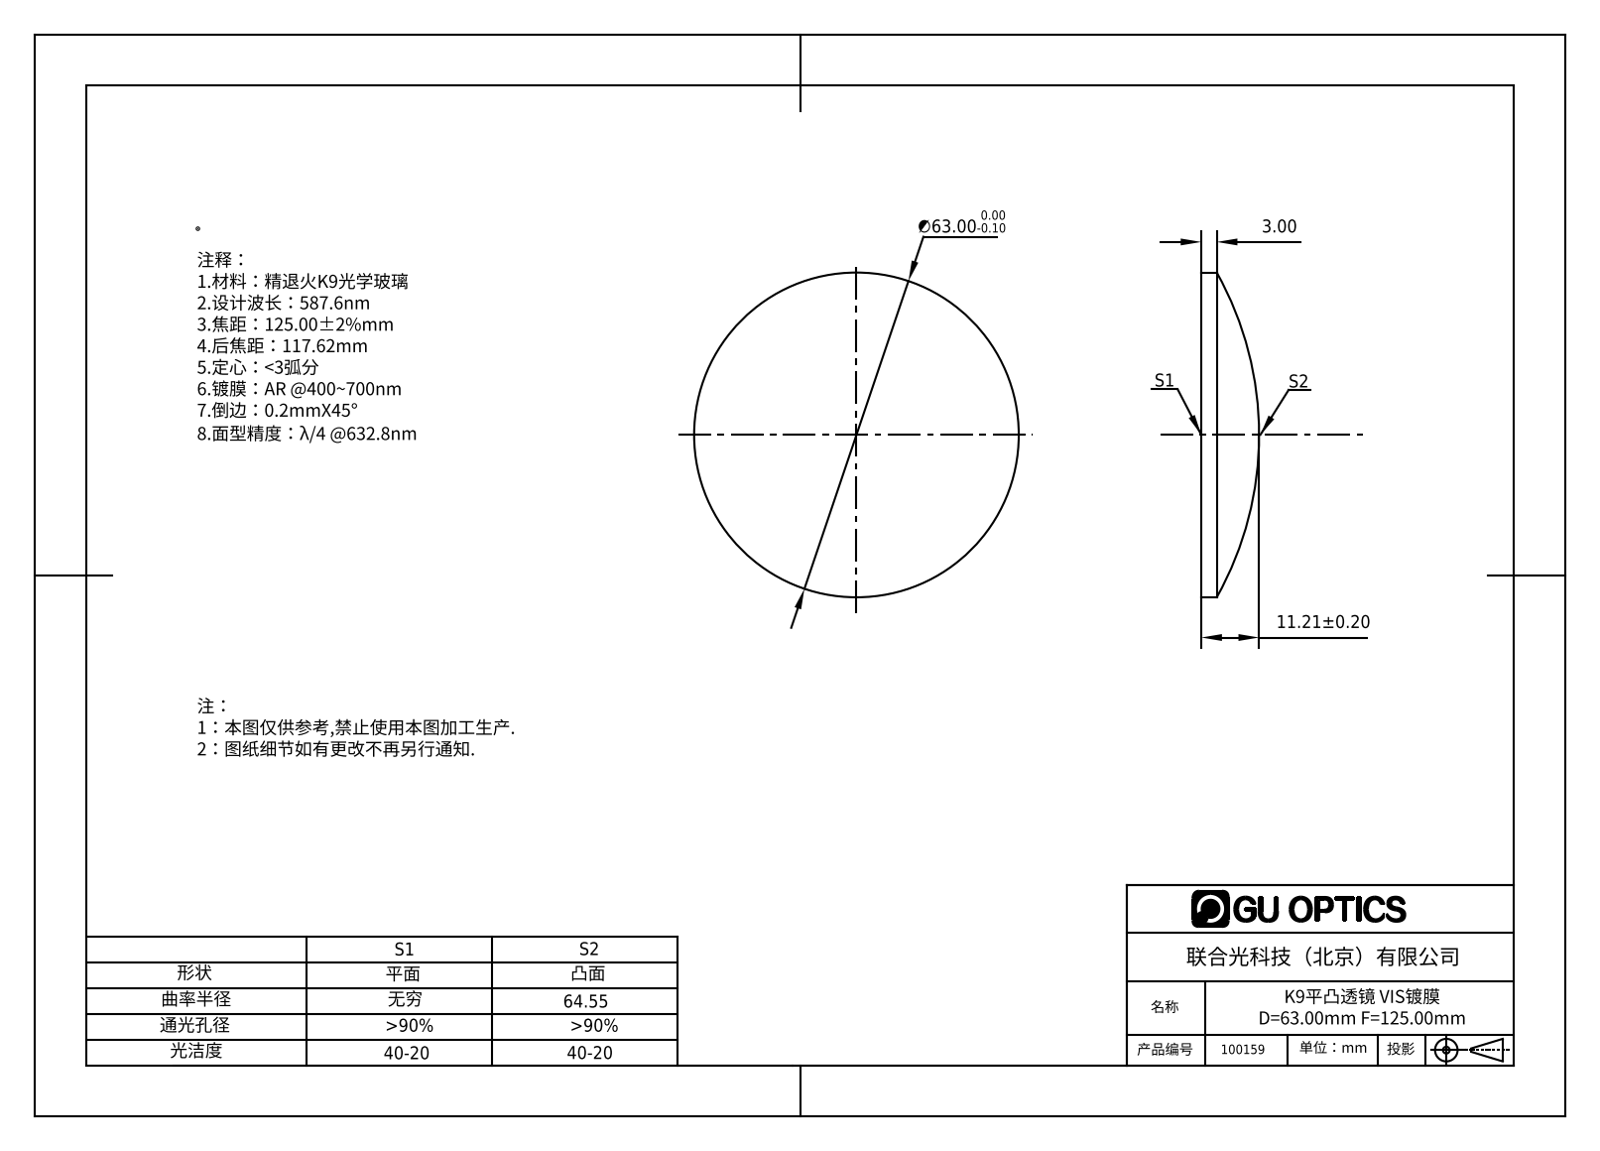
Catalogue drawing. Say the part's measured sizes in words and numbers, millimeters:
The part is named "100159". Its 3-D file was written by "SolidWorks 2016 (AUTOMOTIVE_DESIGN)". It is 1 solid with 5 faces: 1 planar, 2 cylindrical and 2 other. Overall it measures 63 by 63 by 11.21 millimeters. Its volume is 22 438 cubic millimeters and its surface area 7 040 square millimeters. Round bosses or shafts: 1 of diameter 63.
